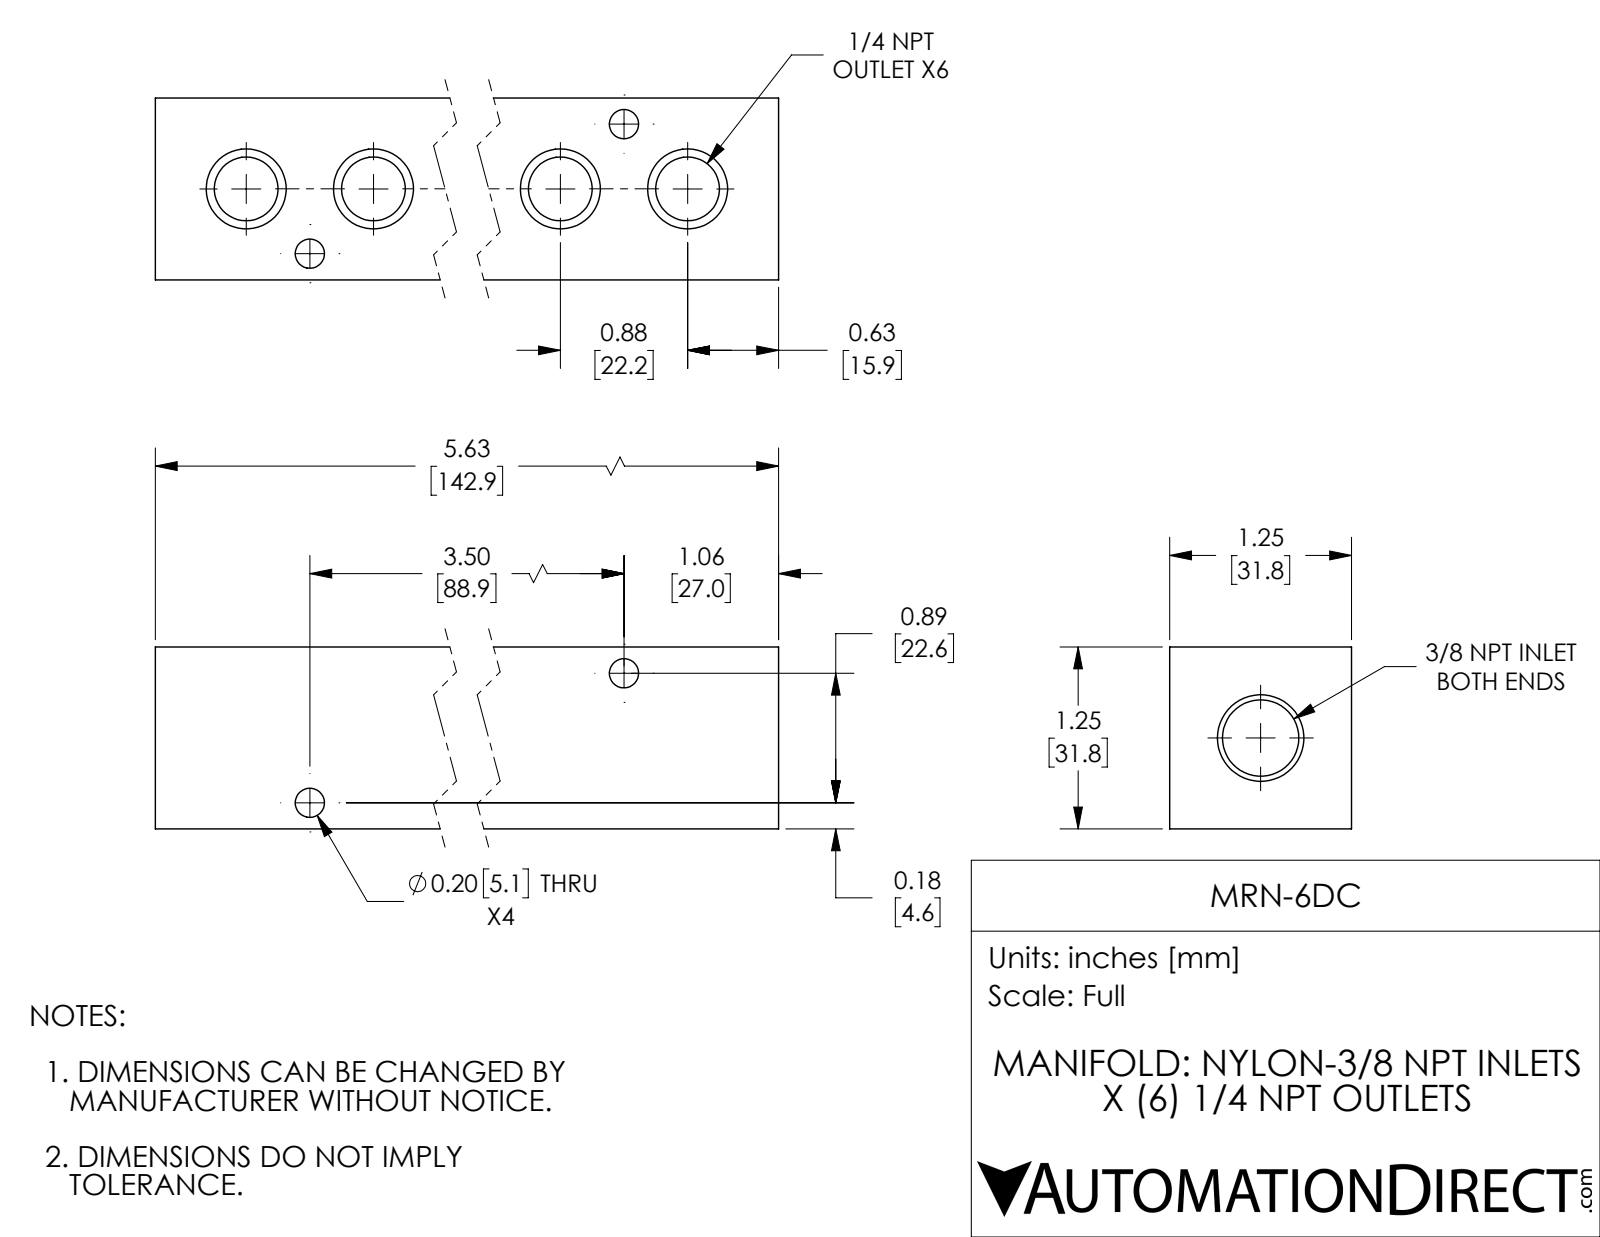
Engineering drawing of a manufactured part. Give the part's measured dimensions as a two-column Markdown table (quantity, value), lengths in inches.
| quantity | value |
| --- | --- |
| part name | MRN-6DC |
| STEP written by | SolidWorks 2018 (AUTOMOTIVE_DESIGN) |
| units | inches |
| bodies | 1 solid, 52 faces (6 planar, 30 cylindrical, 16 other) |
| overall size | 5.625 × 1.25 × 1.25 |
| volume | 7.057 in³ |
| surface area | 43.89 in² |
| round holes (diameter × count) | 0.438 × 6, 0.201 × 4, 0.525 × 1 |
| main face-to-face distances | 1.25, 5.625 |
| hole center spacings | 0.624, 0.875, 1.75, 0.875, 2.625, 3.611, 3.963, 1.385 |
